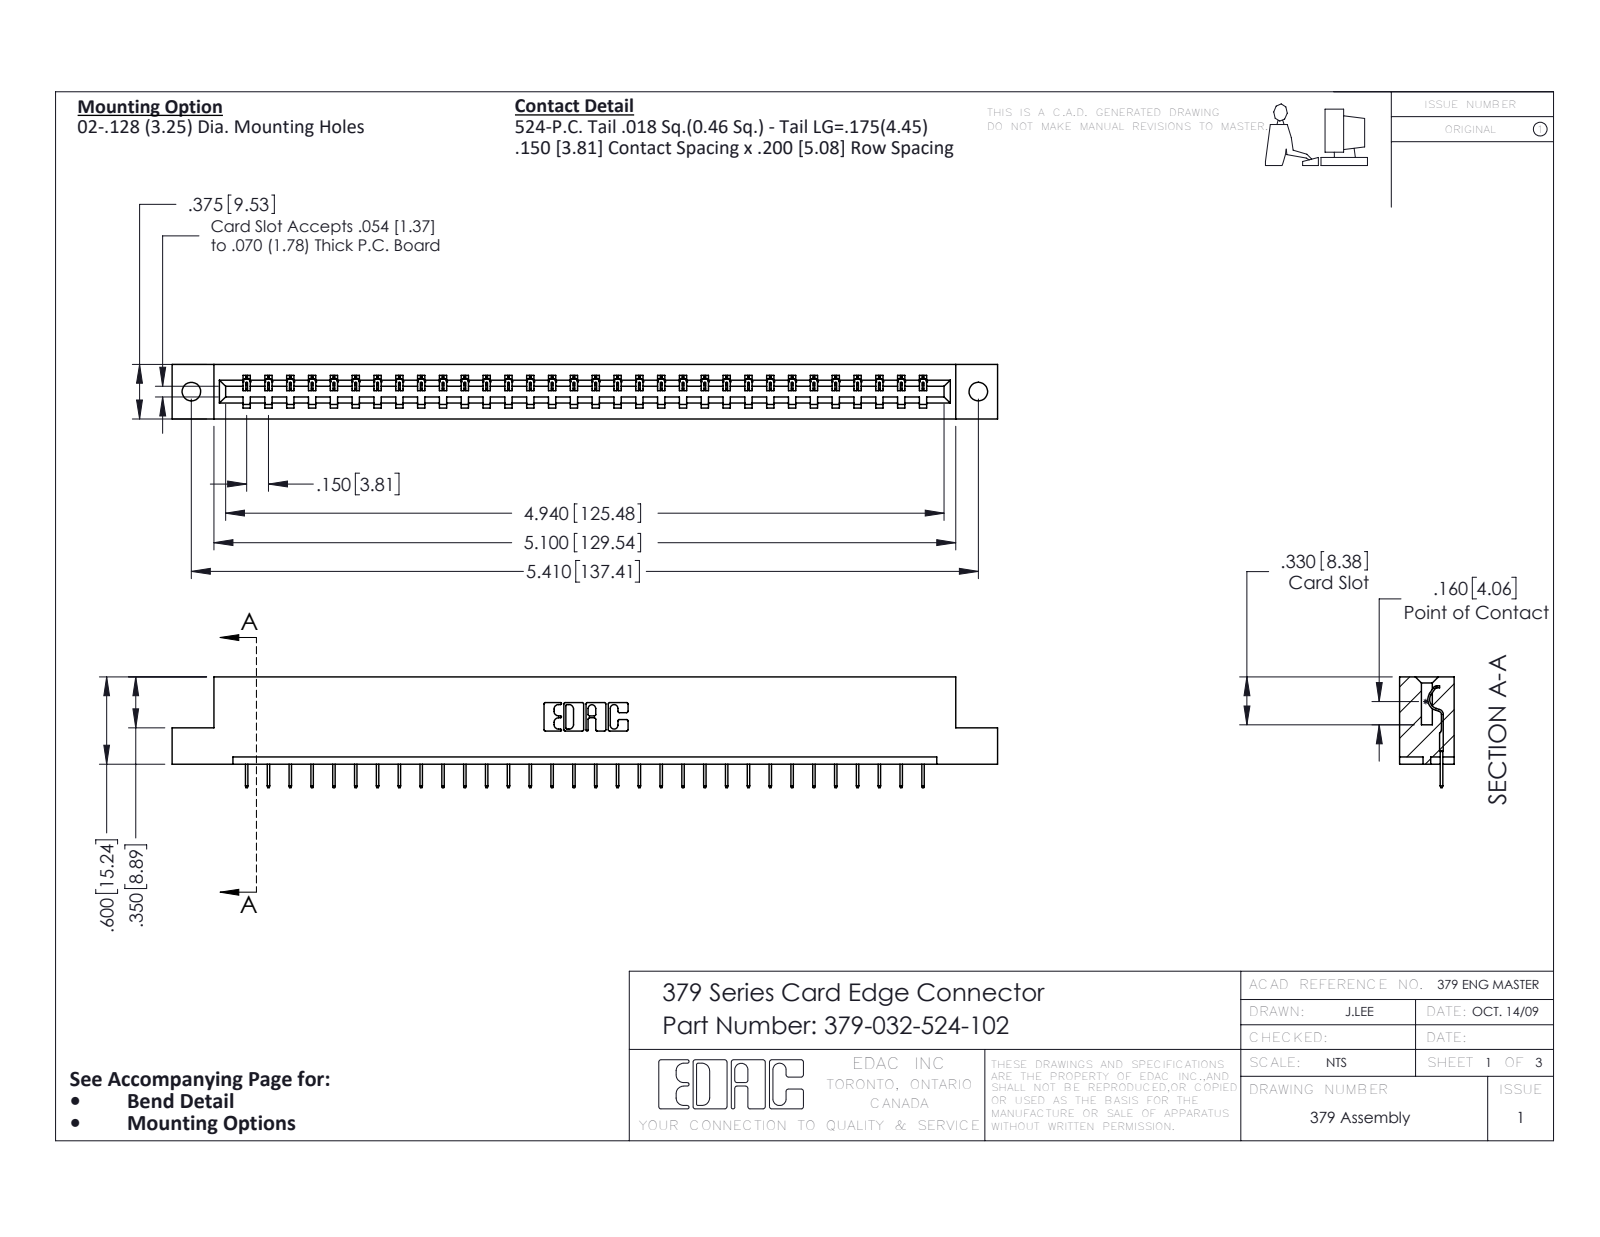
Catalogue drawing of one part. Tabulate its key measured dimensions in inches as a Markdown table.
| quantity | value |
| --- | --- |
| part name | 379-032-524-102; 345-292-001_345-293-124; 379 Part_Flush - .128 Dia |
| STEP written by | SolidWorks 2016 (CONFIG_CONTROL_DESIGN) |
| units | inches |
| bodies | 33 solids, 2098 faces (1606 planar, 492 cylindrical, 0 other) |
| overall size | 5.675 × 0.762 × 0.375 |
| volume | 0.907 in³ |
| surface area | 22.38 in² |
| round holes (diameter × count) | 0.128 × 2 |
| partial cylindrical surfaces (radius × count) | 0.006 × 64, 0.01 × 22, 0.007 × 6, 0.031 × 6, 0.026 × 3, 0.014 × 1, 0.022 × 1, 0.024 × 1 |
| main face-to-face distances | 0.3, 0.075, 0.375, 0.225, 0.6, 0.2, 0.55, 0.15, 0.15, 0.15 |
| hole center spacings | 5.41 |
